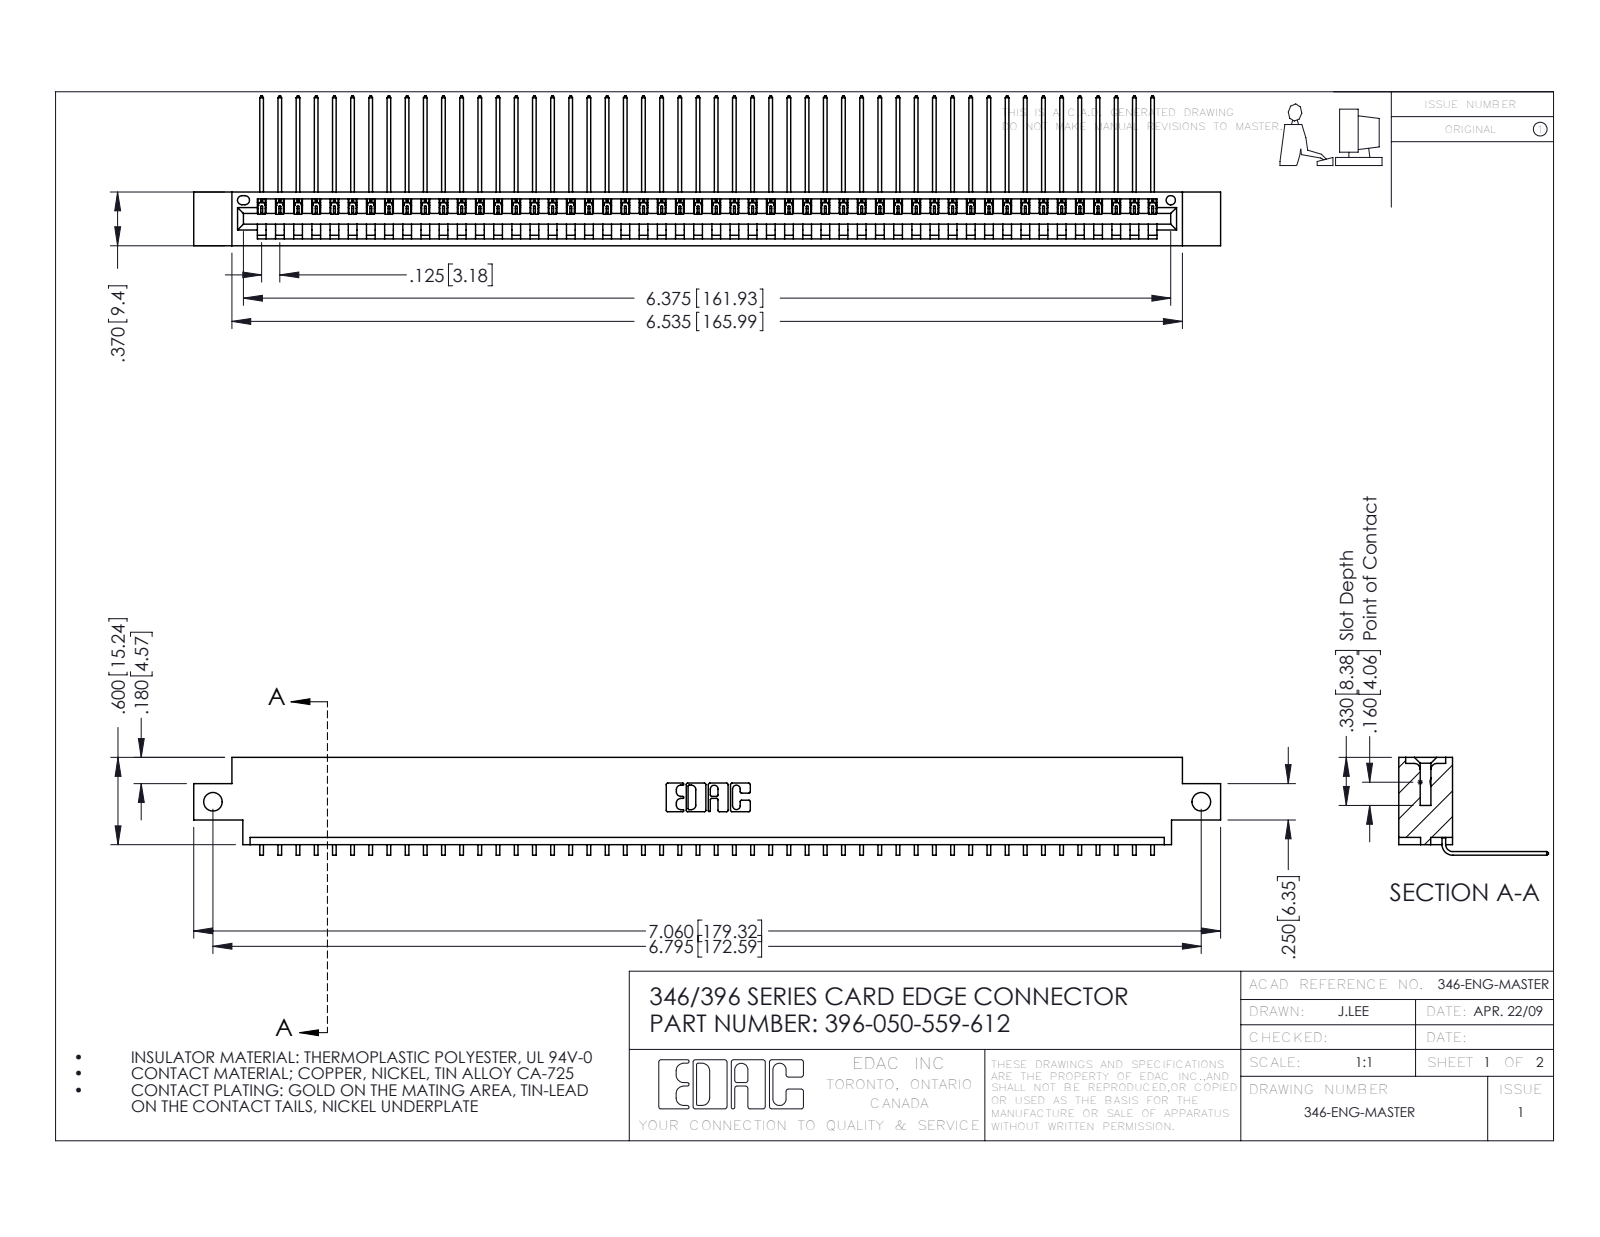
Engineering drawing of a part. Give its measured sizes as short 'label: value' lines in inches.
name: 396-050-559-612; 345-292-001_558 559 Tail - 1; 346 Part_0.170 Offset - Side Mount
written by: SolidWorks 2016 (CONFIG_CONTROL_DESIGN)
unit: in
bodies: 51 solids, 3126 faces (2180 planar, 946 cylindrical, 0 other)
size: 7.06 × 1.03 × 0.673
volume: 1.046 in³; area: 34.91 in²
holes: 2× ⌀0.128, 1× ⌀0.064
rounds: 100× R0.006, 22× R0.01, 6× R0.007, 6× R0.031, 3× R0.026, 2× R0.031, 2× R0.04, 1× R0.014
face distances: 0.048, 0.322, 0.37, 0.025, 0.25, 0.072, 0.298, 0.148, 0.222, 0.1
hole spacings: 6.795
